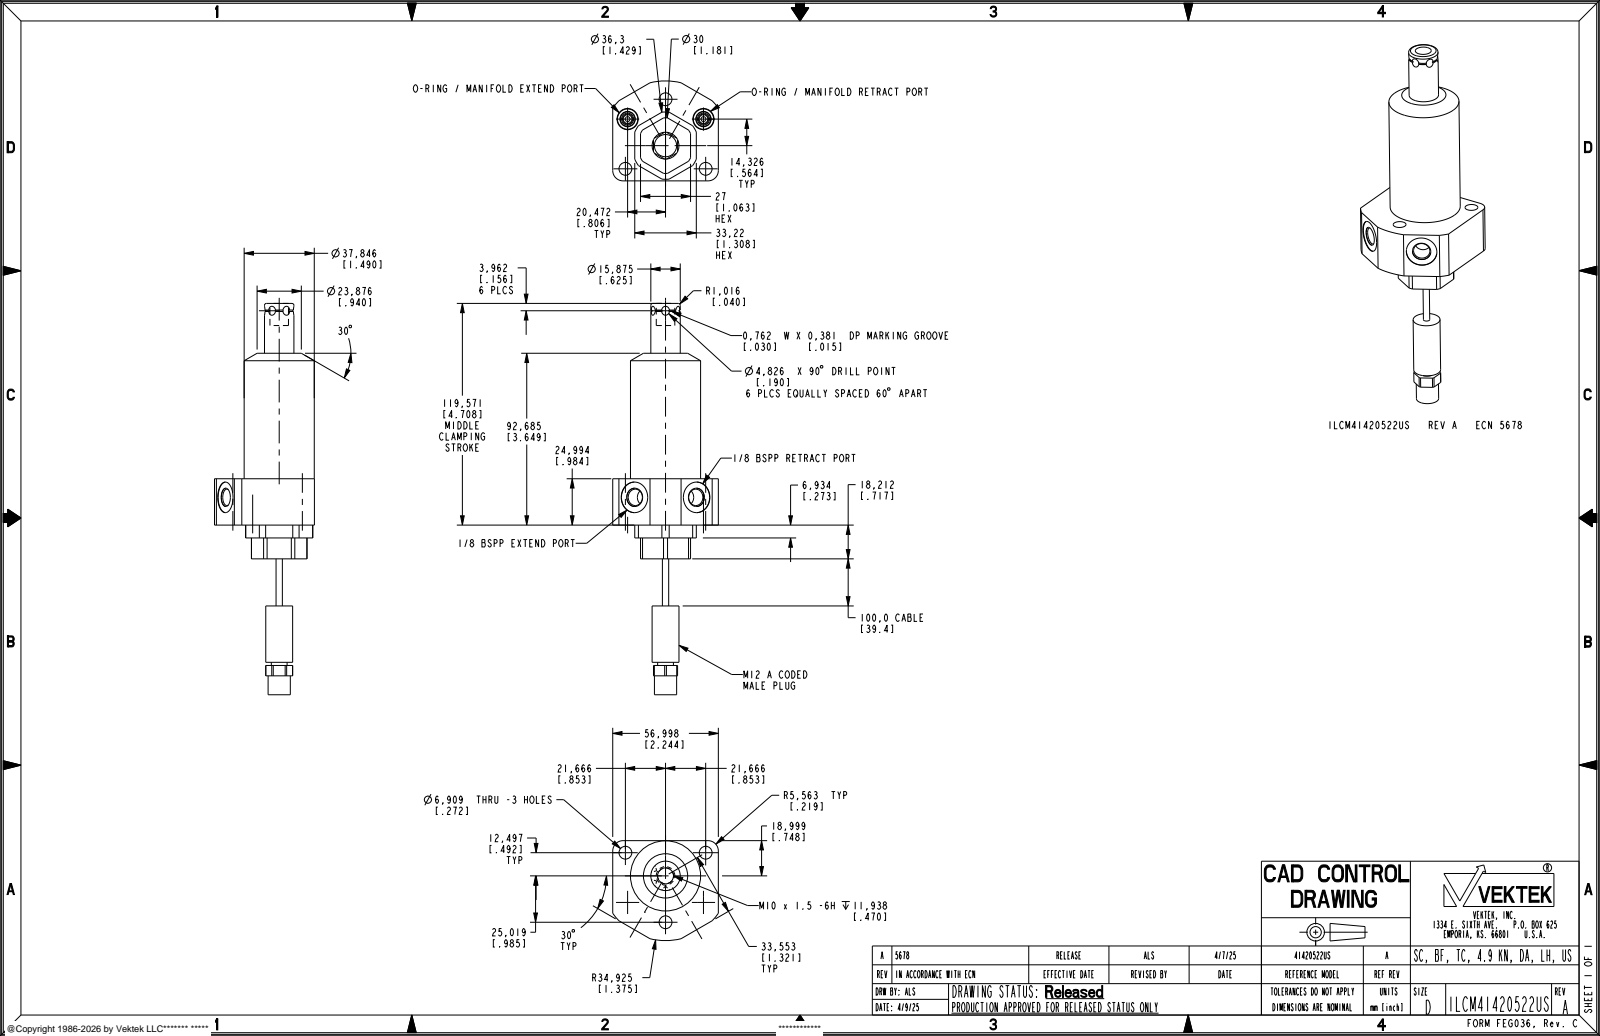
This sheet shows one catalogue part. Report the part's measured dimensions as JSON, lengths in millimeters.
{"part_name": "ILCM41420522US", "step_written_by": "CREO PARAMETRIC BY PTC INC, 2021164 (AUTOMOTIVE_DESIGN)", "units": "millimeters", "bodies": {"solids": 1, "faces": 194, "planar": 79, "cylindrical": 81, "other": 34}, "overall_size": [211.09, 69.92, 65], "volume_mm3": 164663, "surface_area_mm2": 27760, "round_holes": [[6.91, 3], [2.49, 2], [6.5, 2], [8.84, 2], [9.91, 2], [11.4, 2], [16.5, 2], [8.61, 1]], "round_bosses_or_shafts": [[5.49, 2], [37.85, 1], [15.88, 1], [14.5, 1], [11.99, 1], [10.01, 1], [8.51, 1], [3.4, 1]], "partial_cylinders_radius": [[5.56, 2], [7.56, 1], [15, 1], [18.15, 1], [34.92, 1]], "face_to_face_distances": [24.99, 57, 18.22, 43.21, 3.11, 30.11, 27, 11.28, 6.94, 31.93], "hole_center_spacings": [25.02, 23.09, 24.99, 26.86, 43.33, 49.96, 40.94, 43.34]}
